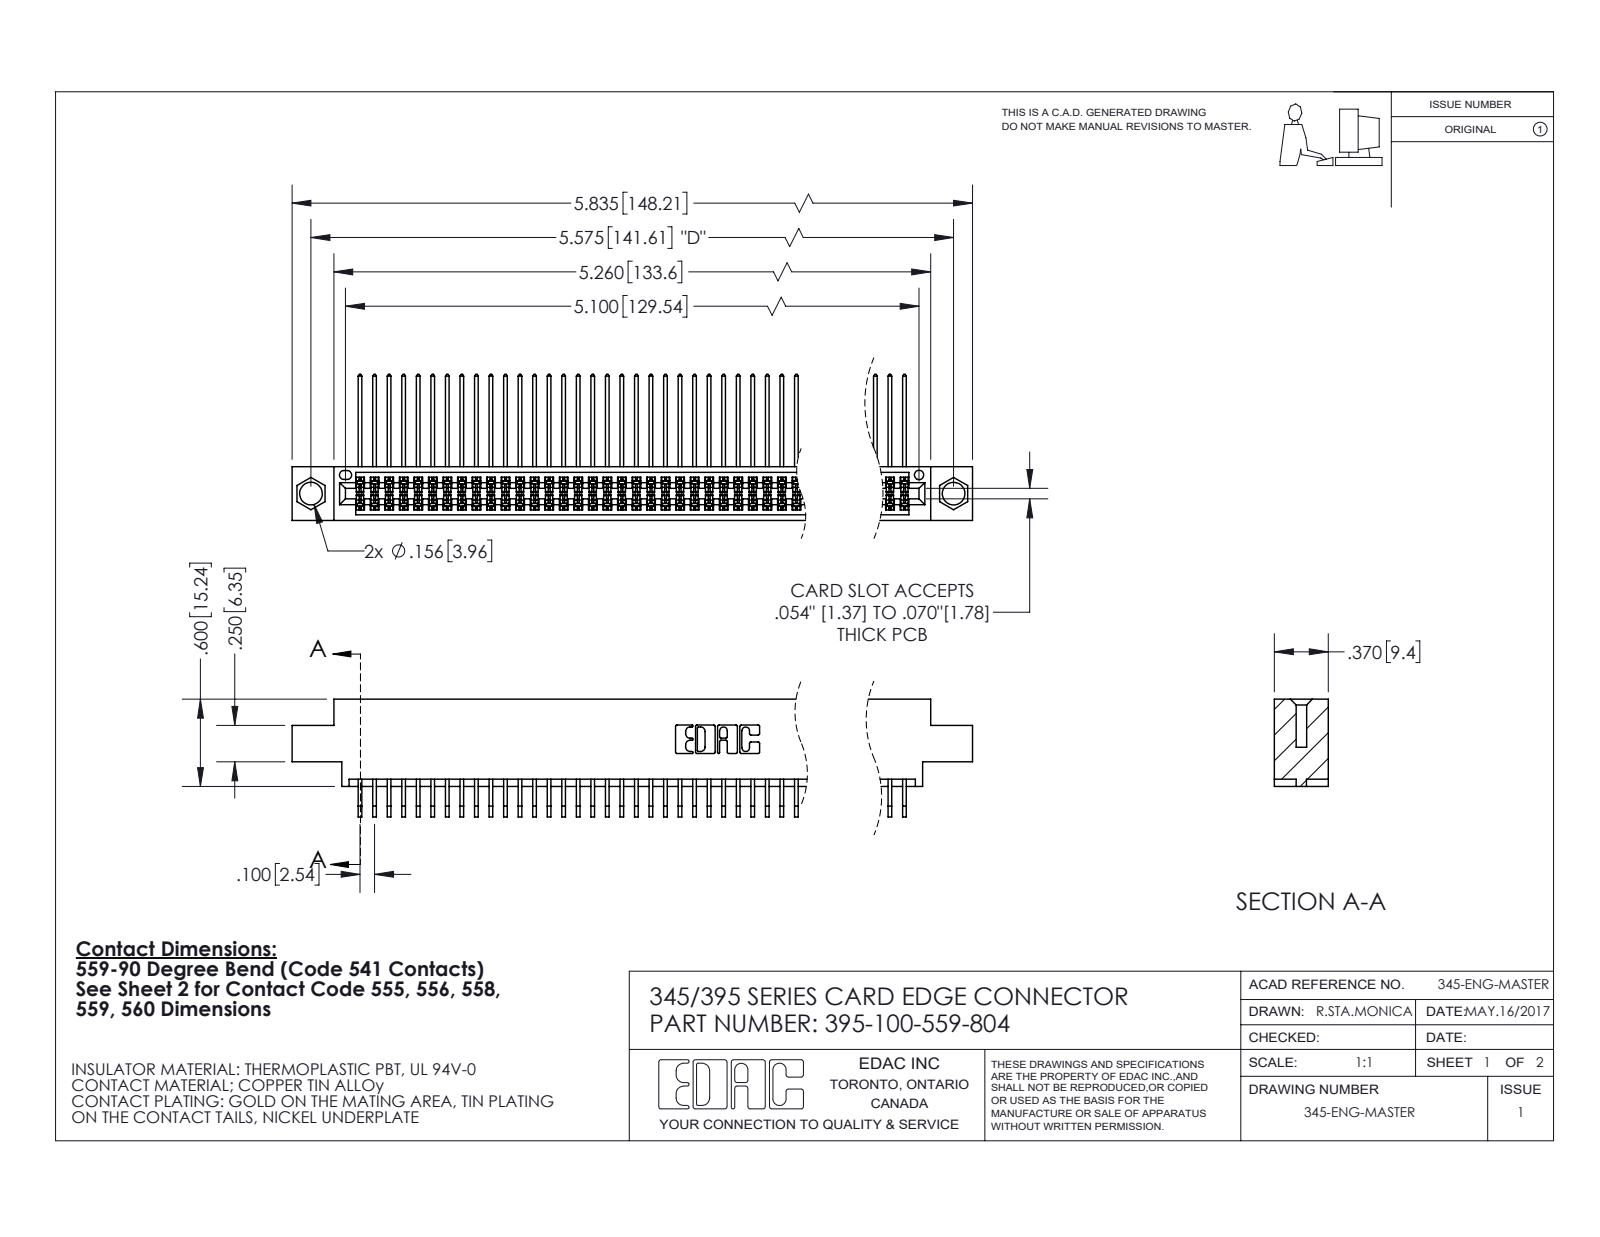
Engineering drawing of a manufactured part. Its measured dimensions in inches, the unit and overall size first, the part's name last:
Units: inches
Overall size (bounding box): 5.835 × 1.005 × 0.809
Round holes (diameter × count): ⌀0.156 ×2, ⌀0.064 ×1
Partial cylindrical surfaces — rounded edges, fillets, slot ends (radius × count): R0.006 ×150, R0.01 ×22, R0.007 ×6, R0.031 ×6, R0.026 ×3, R0.014 ×2, R0.019 ×2, R0.022 ×2
Main face-to-face distances: 0.072, 0.298, 0.37, 0.2, 0.098, 0.272, 0.025, 0.225, 0.175, 0.15
Hole centre spacings: 0.27, 5.339, 5.575
Volume: 0.905 in³ · Surface area: 38.41 in²
Bodies: 101 solids, 5344 faces (3598 planar, 1746 cylindrical, 0 other)
Part name (STEP PRODUCT): 345-292-001_558 559 Tail - 1; 345-292-001_559 Tail - 2; 395-100-559-804; 345 Part_0.170 Offset - 0.156 Dia-TI
STEP written by: SolidWorks 2020 (CONFIG_CONTROL_DESIGN)
